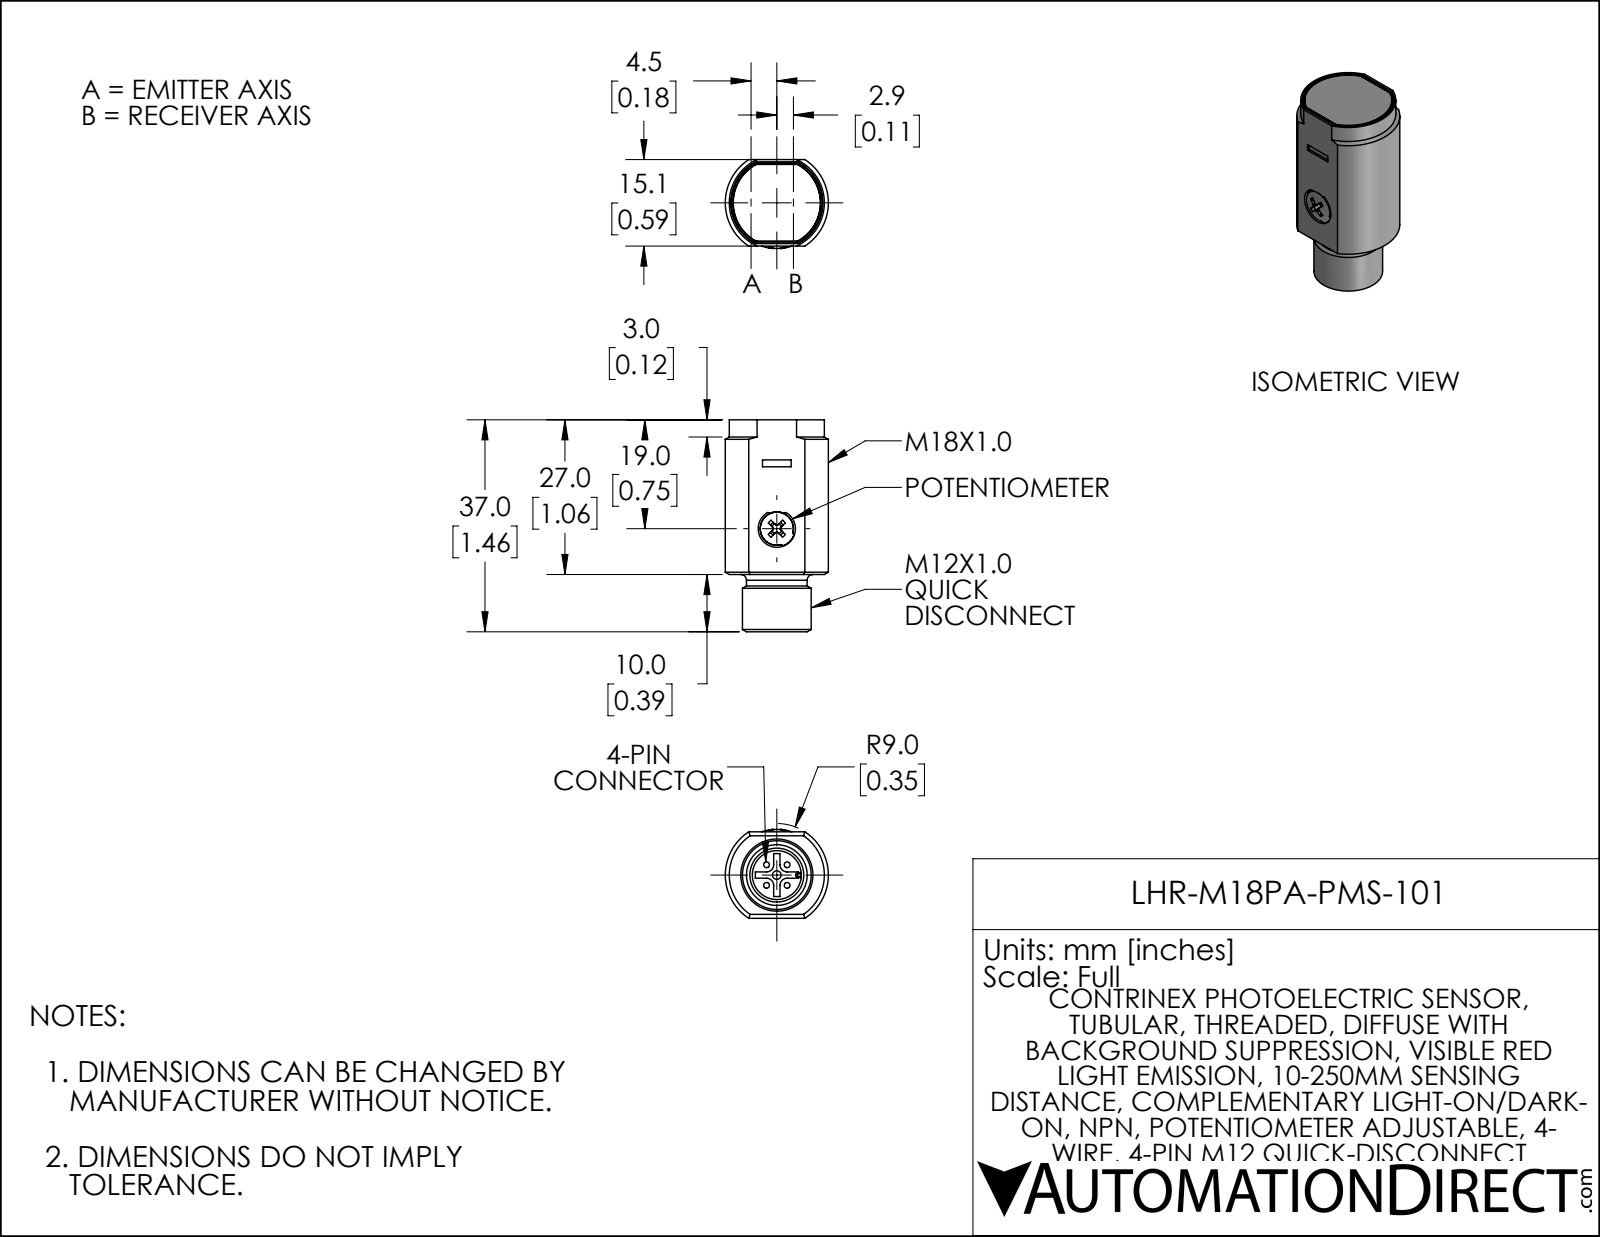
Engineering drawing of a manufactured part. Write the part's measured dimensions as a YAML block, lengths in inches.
part_name: "LHR-M18PA-PMS-101"
step_written_by: "SolidWorks 2021 (AUTOMOTIVE_DESIGN)"
units: inches
bodies: {solids: 1, faces: 148, planar: 75, cylindrical: 53, other: 20}
overall_size: [1.457, 0.709, 0.611]
volume: 0.417
surface_area: 4.272
round_holes:
  - {diameter: 0.059, count: 1}
  - {diameter: 0.256, count: 1}
  - {diameter: 0.336, count: 1}
round_bosses_or_shafts:
  - {diameter: 0.039, count: 4}
  - {diameter: 0.472, count: 1}
  - {diameter: 0.417, count: 1}
partial_cylinders:
  - {radius: 0.014, count: 8}
  - {radius: 0.028, count: 8}
  - {radius: 0.006, count: 4}
  - {radius: 0.024, count: 4}
  - {radius: 0.049, count: 4}
  - {radius: 0.008, count: 2}
  - {radius: 0.017, count: 1}
  - {radius: 0.116, count: 1}
face_to_face_distances: [0.594, 1.061, 0.047, 1.108, 0.016, 1.063, 1.11, 1.457, 1.455, 0.394]
